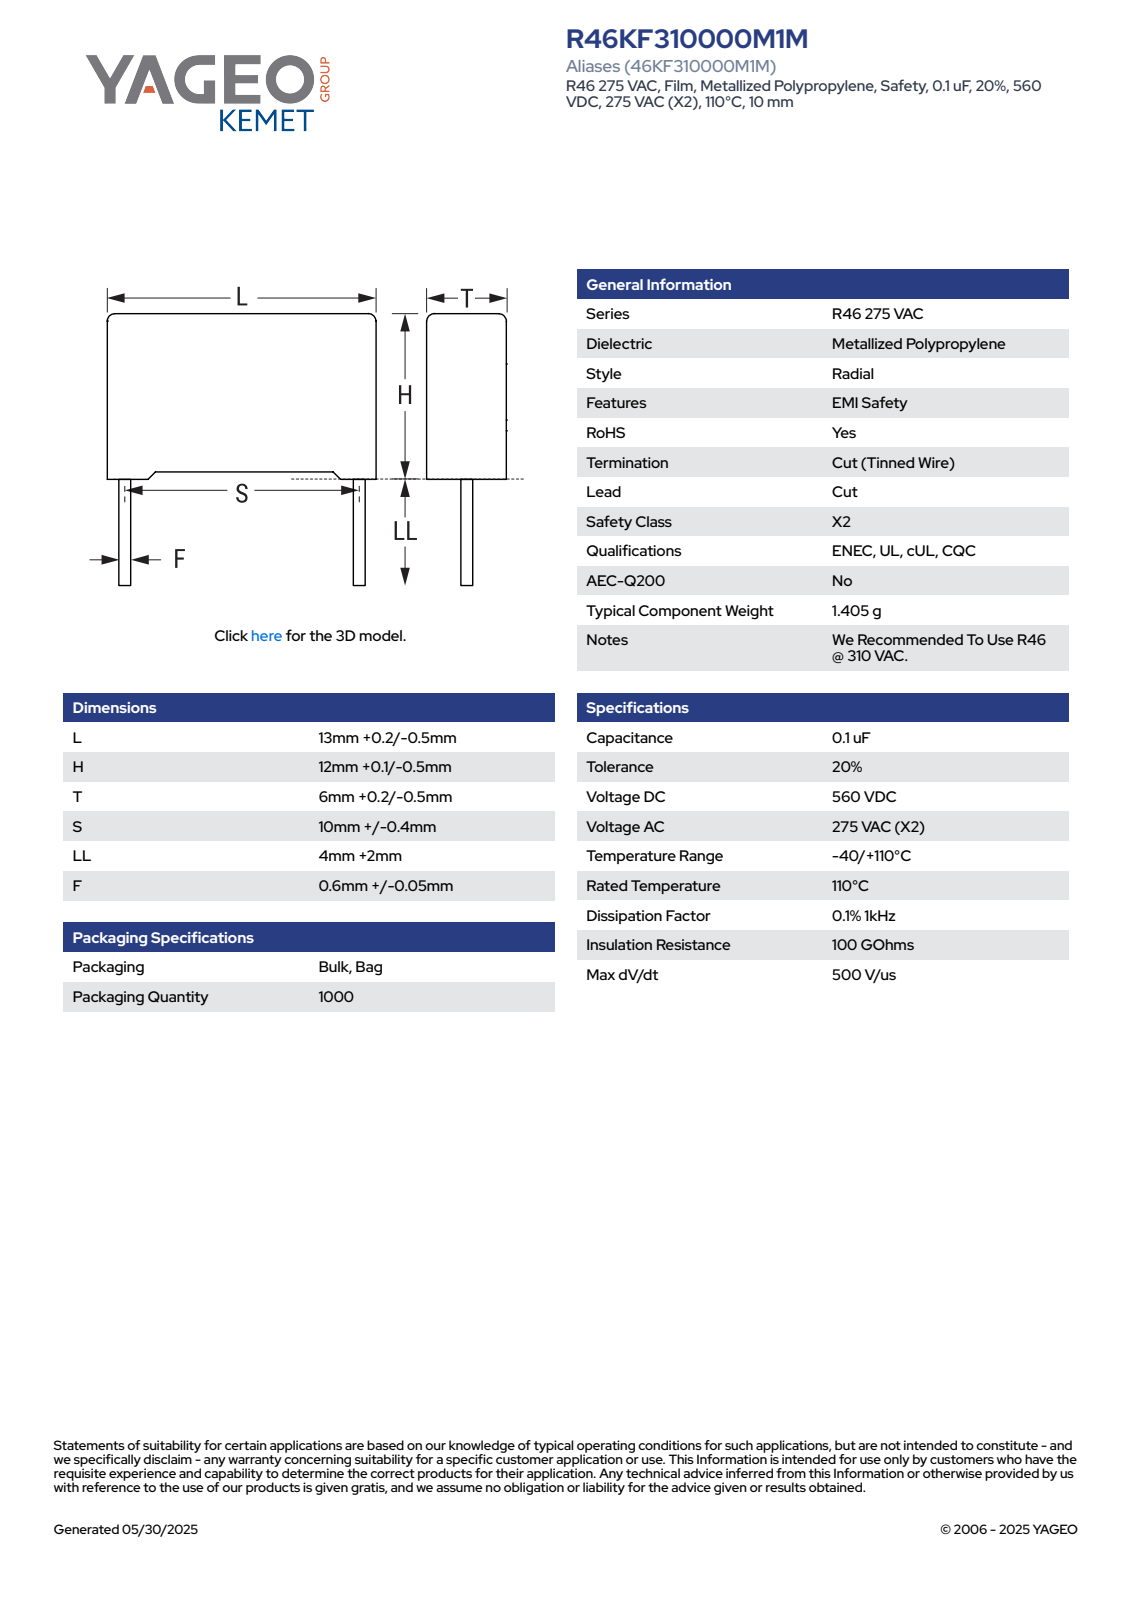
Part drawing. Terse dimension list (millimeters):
name: CFR_RB2_13X12X6_L13.2H12.1T6.2S10LL6F0.65
written by: SolidWorks 2021 (AUTOMOTIVE_DESIGN)
unit: mm
bodies: 4 solids, 85 faces (77 planar, 8 cylindrical, 0 other)
size: 18.1 × 13.2 × 6.21
volume: 941 mm³; area: 681 mm²
bosses: 2× ⌀0.65
rounds: 4× R0.5
face distances: 6.2, 13.2, 11.35, 0.44, 5.76, 0.75, 12.1, 12.76, 5.32, 0.42
